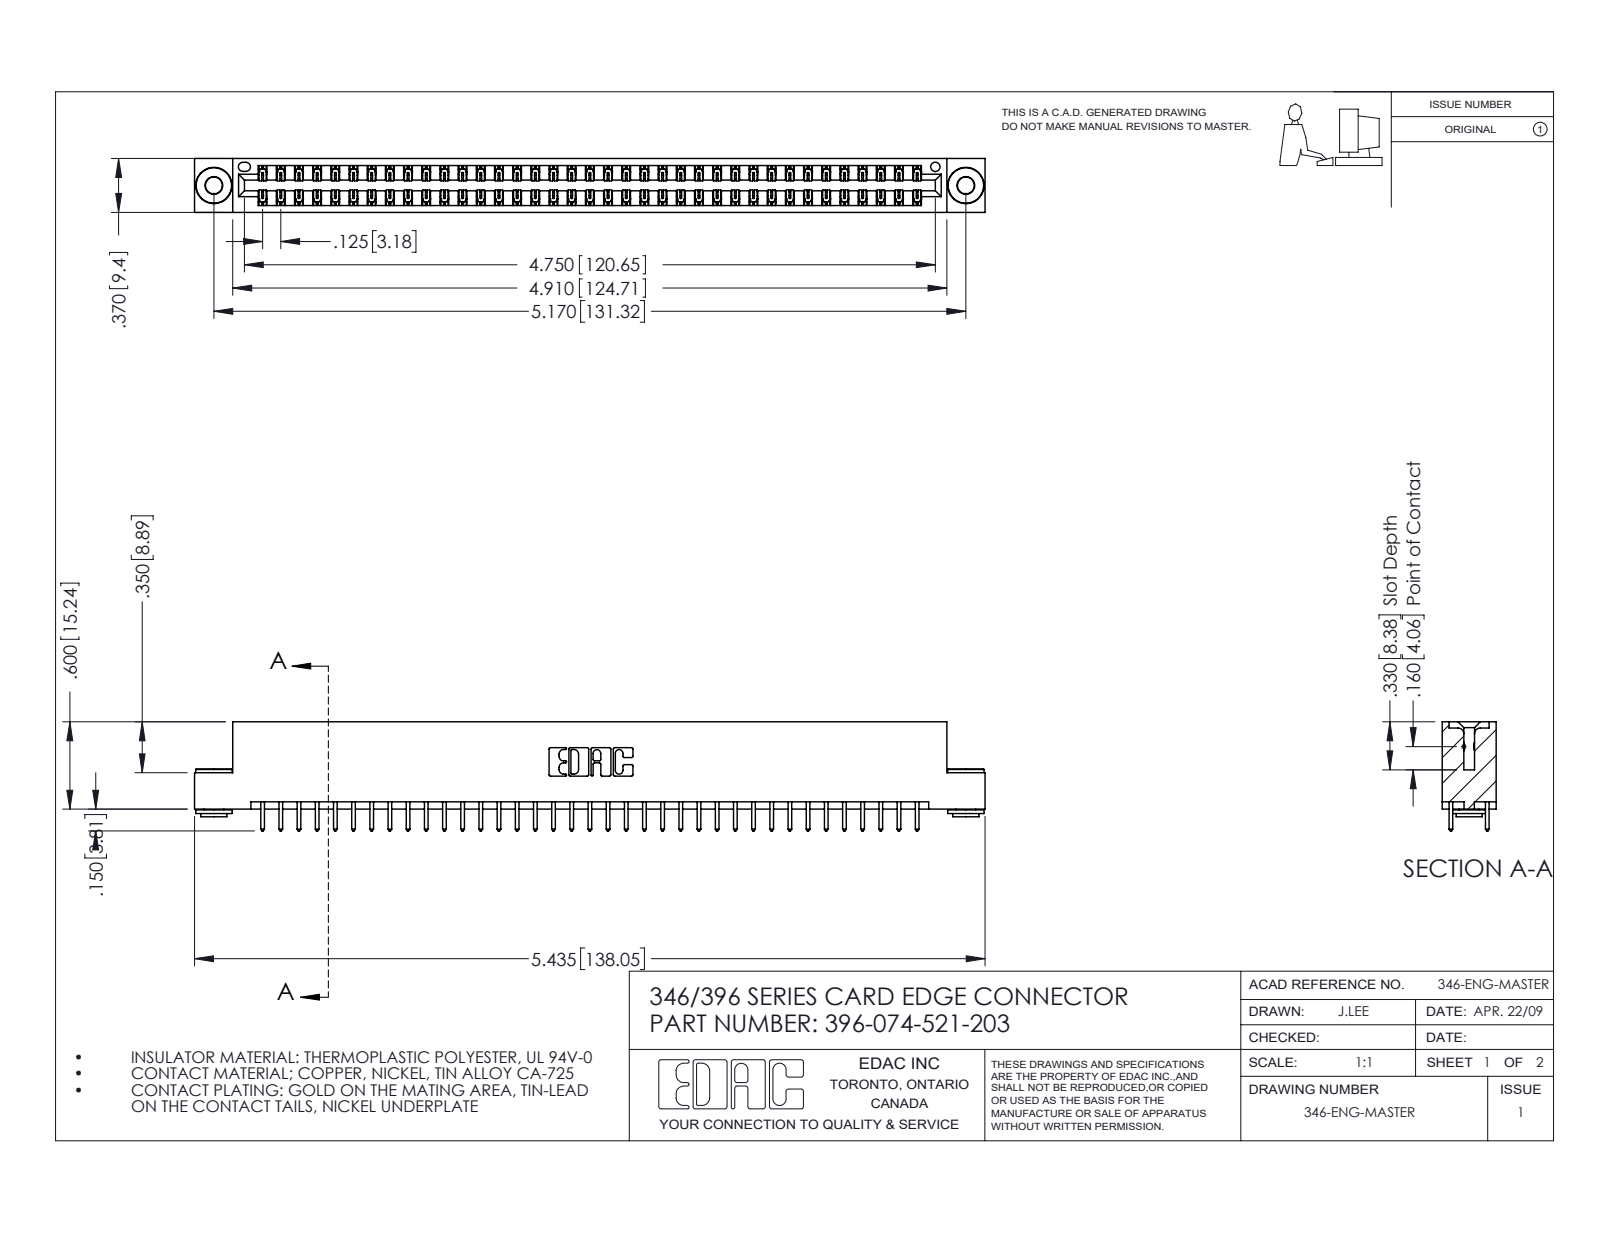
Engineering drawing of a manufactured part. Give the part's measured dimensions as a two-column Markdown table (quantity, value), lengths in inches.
| quantity | value |
| --- | --- |
| part name | 345-292-001_345-293-121; 346 Part_Flush Mounting Lugs - 0.156 Dia-TH; 345-250-002_345-250-002-102; 396-074-521-203 |
| STEP written by | SolidWorks 2016 (CONFIG_CONTROL_DESIGN) |
| units | inches |
| bodies | 77 solids, 4008 faces (2676 planar, 1324 cylindrical, 8 other) |
| overall size | 5.435 × 0.75 × 0.37 |
| volume | 0.818 in³ |
| surface area | 28.47 in² |
| round holes (diameter × count) | 0.116 × 2, 0.156 × 2, 0.064 × 1 |
| round bosses / shafts (diameter × count) | 0.25 × 2, 0.18 × 2, 0.136 × 2 |
| partial cylindrical surfaces (radius × count) | 0.006 × 111, 0.01 × 74, 0.01 × 22, 0.007 × 6, 0.031 × 6, 0.026 × 3, 0.014 × 2, 0.022 × 2 |
| main face-to-face distances | 0.048, 0.322, 0.25, 0.37, 0.025, 0.072, 0.298, 0.275, 0.148, 0.222 |
| hole center spacings | 0.246, 4.961, 5.17 |
